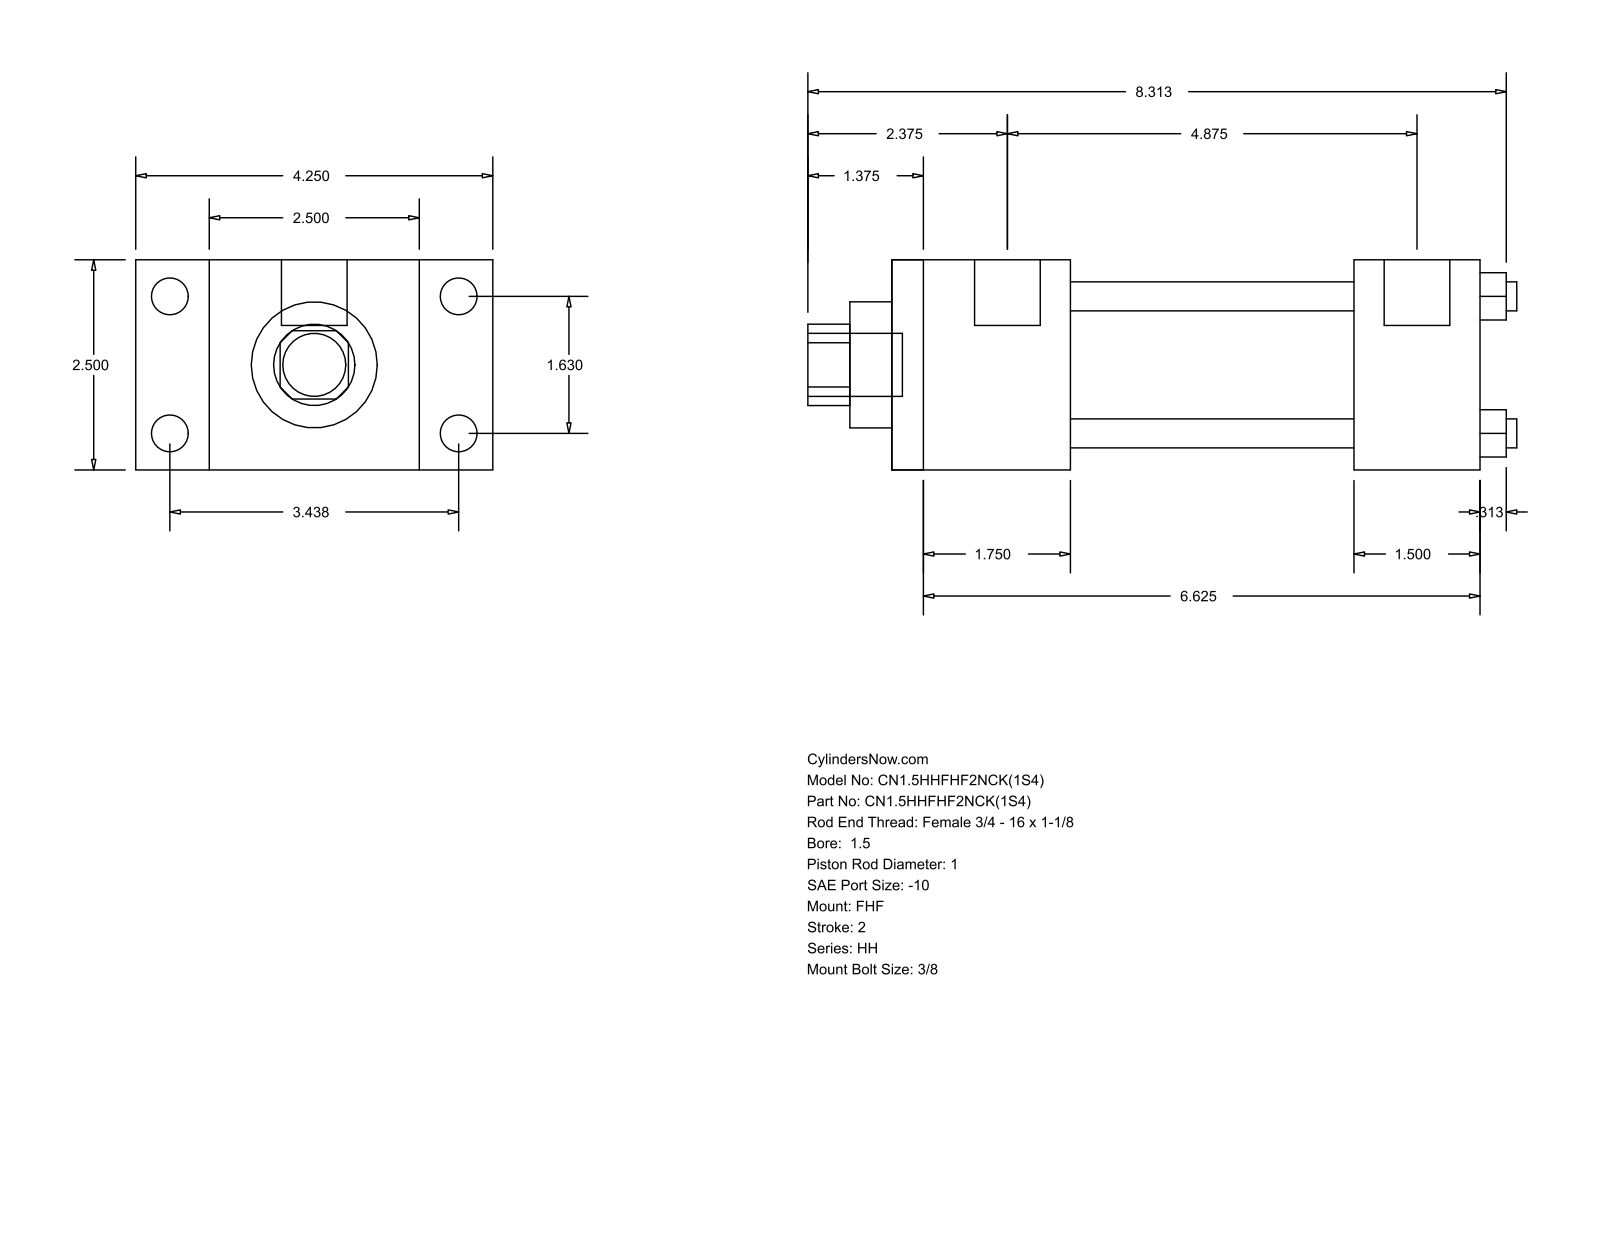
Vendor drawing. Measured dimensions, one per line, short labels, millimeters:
name: HH_FHF__0150_1
written by: GSSL Pune (CONFIG_CONTROL_DESIGN)
unit: mm
bodies: 0 solids, 88 faces (60 planar, 28 cylindrical, 0 other)
size: 214.31 × 107.95 × 63.5
holes: 4× ⌀8.76, 1× ⌀25.4, 1× ⌀38.1, 1× ⌀44.45
bosses: 4× ⌀11.13, 4× ⌀5.56, 2× ⌀19.84, 1× ⌀19.05
rounds: 1× R12.29
face distances: 63.5, 22.23, 85.73, 53.98, 107.96, 177.8, 123.82, 85.72, 139.7, 38.1
hole spacings: 29.27, 41.4, 58.55
